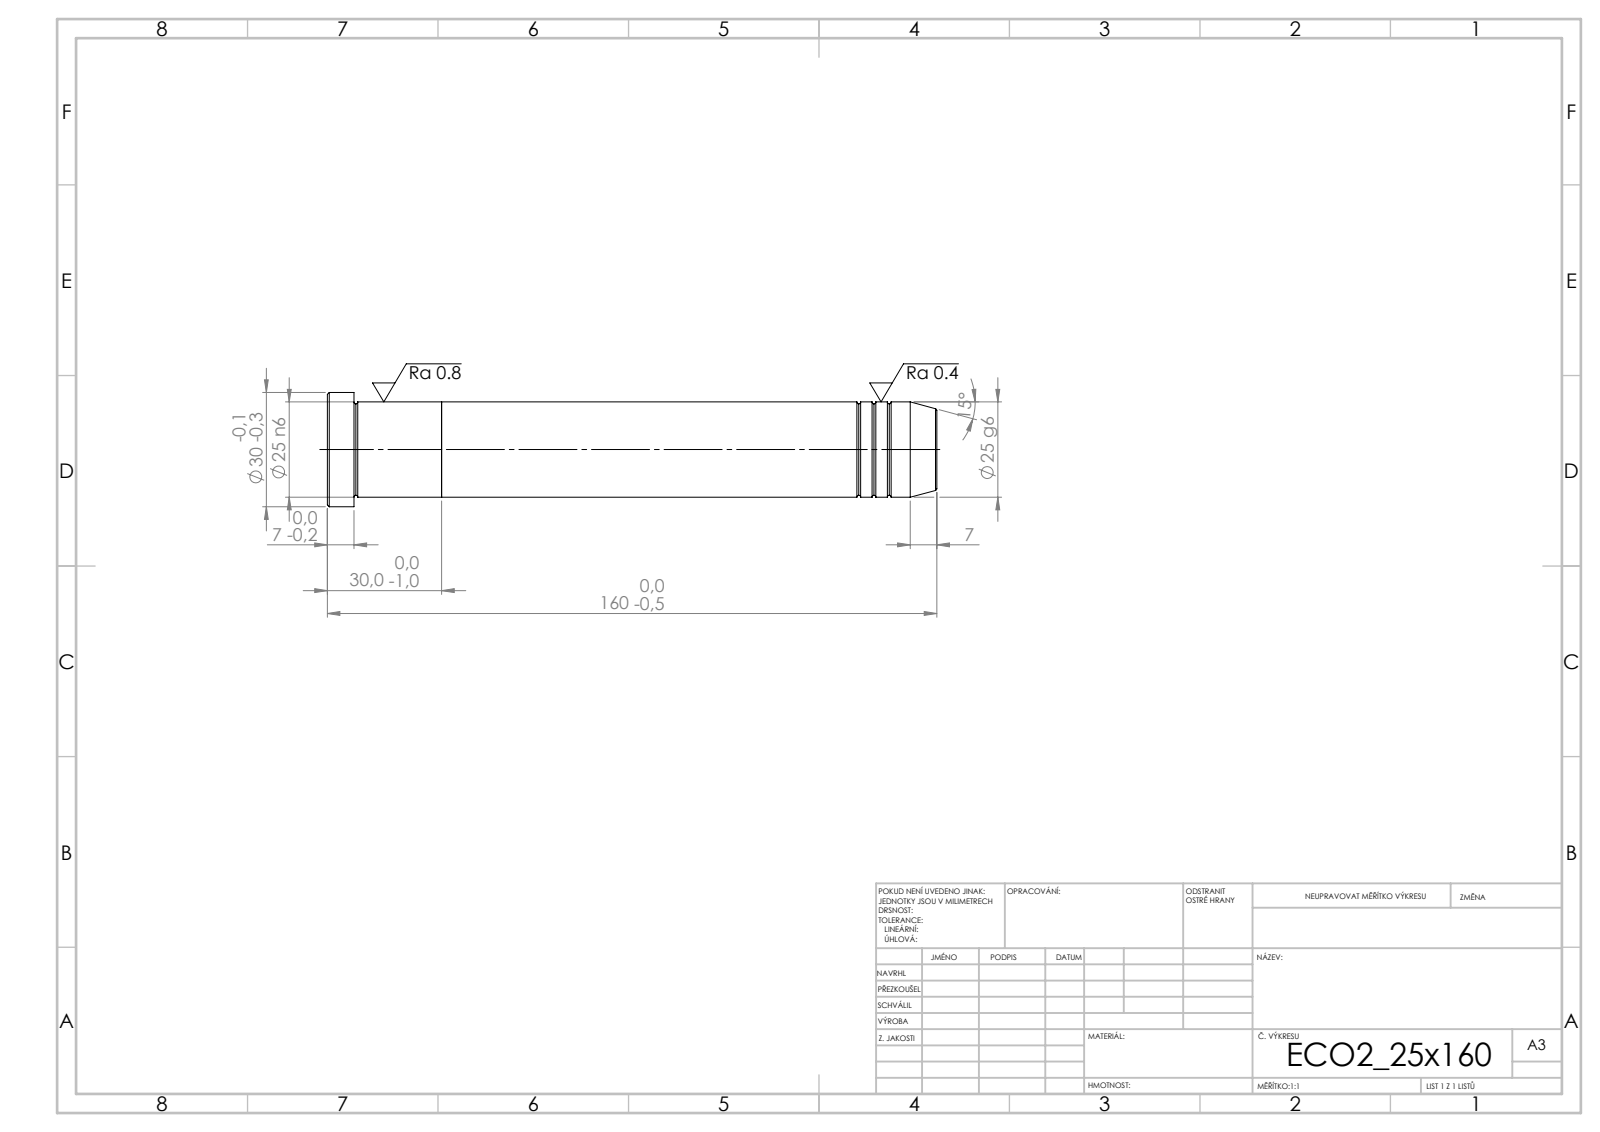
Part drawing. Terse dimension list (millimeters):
written by: SolidWorks 2019 (CONFIG_CONTROL_DESIGN)
unit: mm
bodies: 2 solids, 39 faces (5 planar, 12 cylindrical, 22 other)
size: 160 × 30 × 30
volume: 79 427 mm³; area: 15 043 mm²
bosses: 1× ⌀30, 1× ⌀25
face distances: 30, 130, 160, 153, 23, 7
